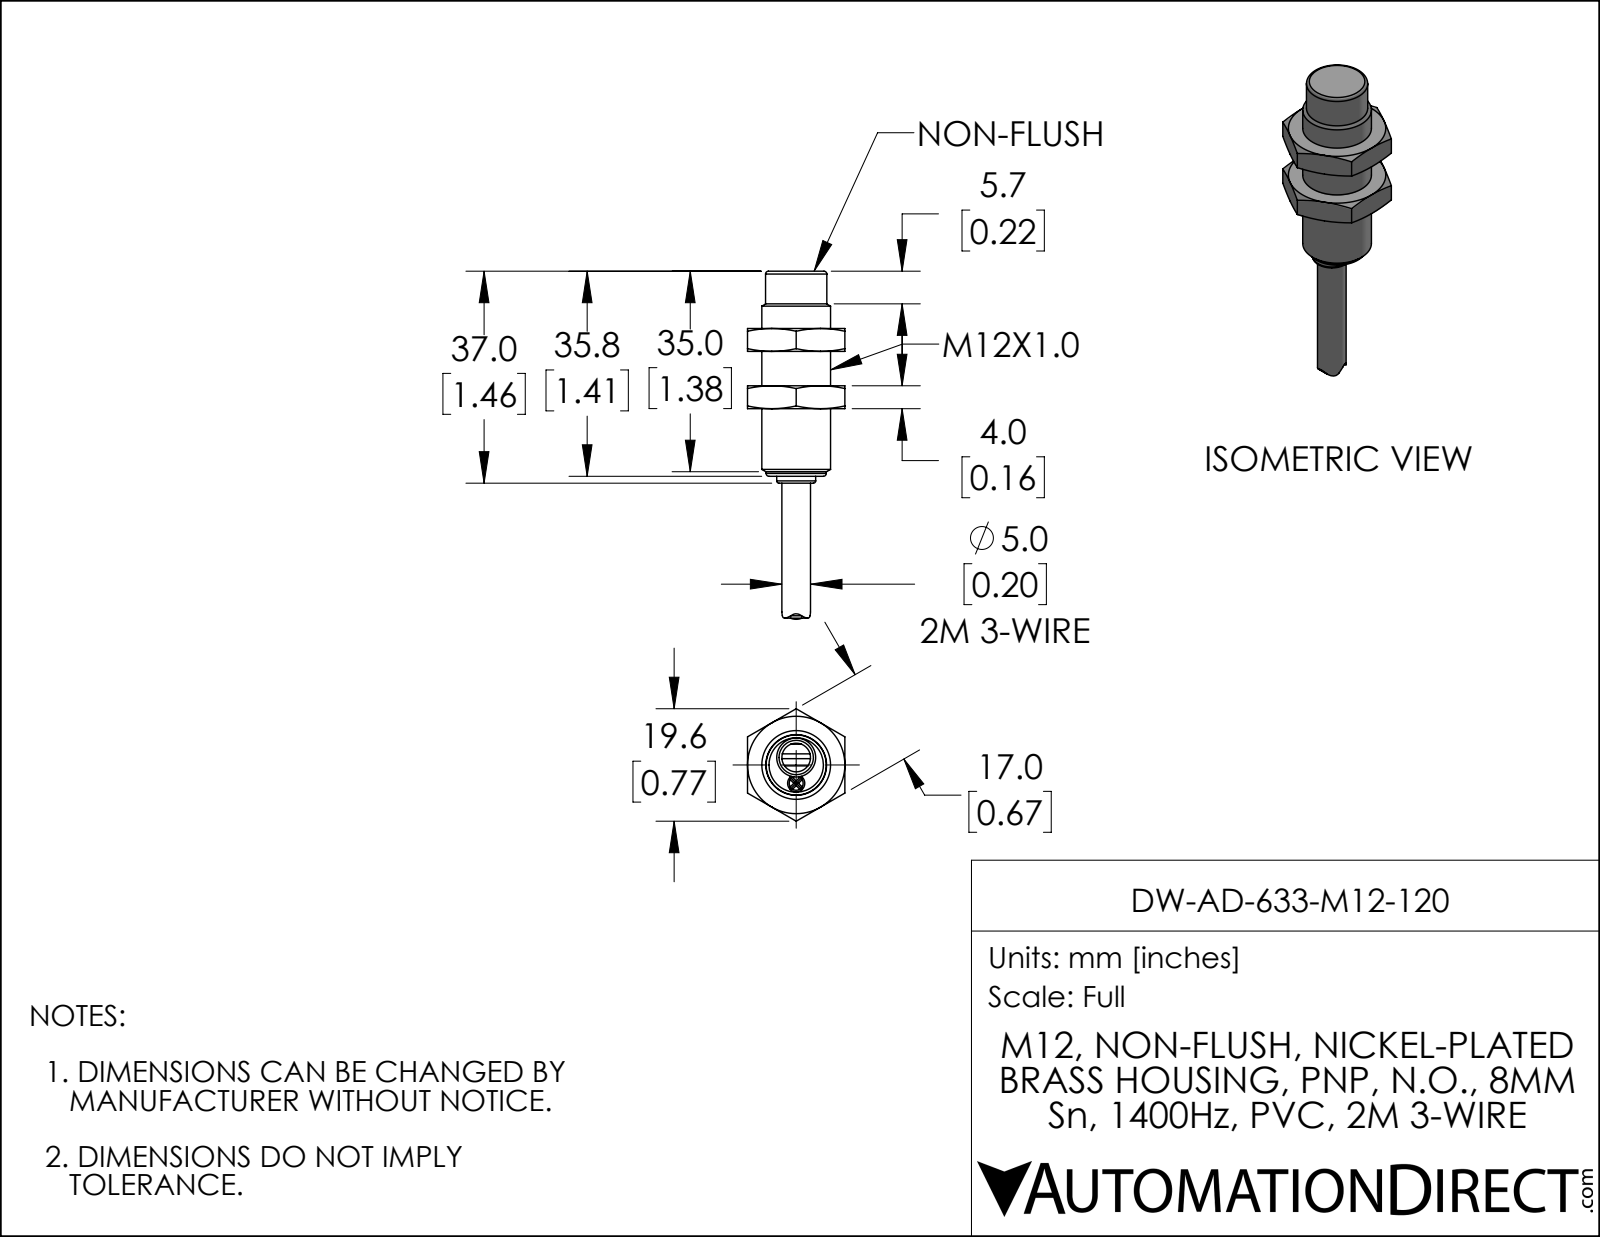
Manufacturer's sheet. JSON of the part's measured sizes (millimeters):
{"part_name": "DW-AD-633-M12-120", "step_written_by": "SolidWorks 2019 (AUTOMOTIVE_DESIGN)", "units": "millimeters", "bodies": {"solids": 1, "faces": 80, "planar": 33, "cylindrical": 13, "other": 34}, "overall_size": [60.8, 19.6, 17], "volume_mm3": 5460, "surface_area_mm2": 2597, "round_bosses_or_shafts": [[12, 1], [10.7, 1], [10.5, 1], [6.8, 1], [5, 1], [3, 1]], "partial_cylinders_radius": [[0.8, 1], [1, 1], [4.2, 1], [6.3, 1], [8.4, 1]], "face_to_face_distances": [10, 4, 17, 14, 6, 20, 24, 35.8, 25.8, 21.8]}
